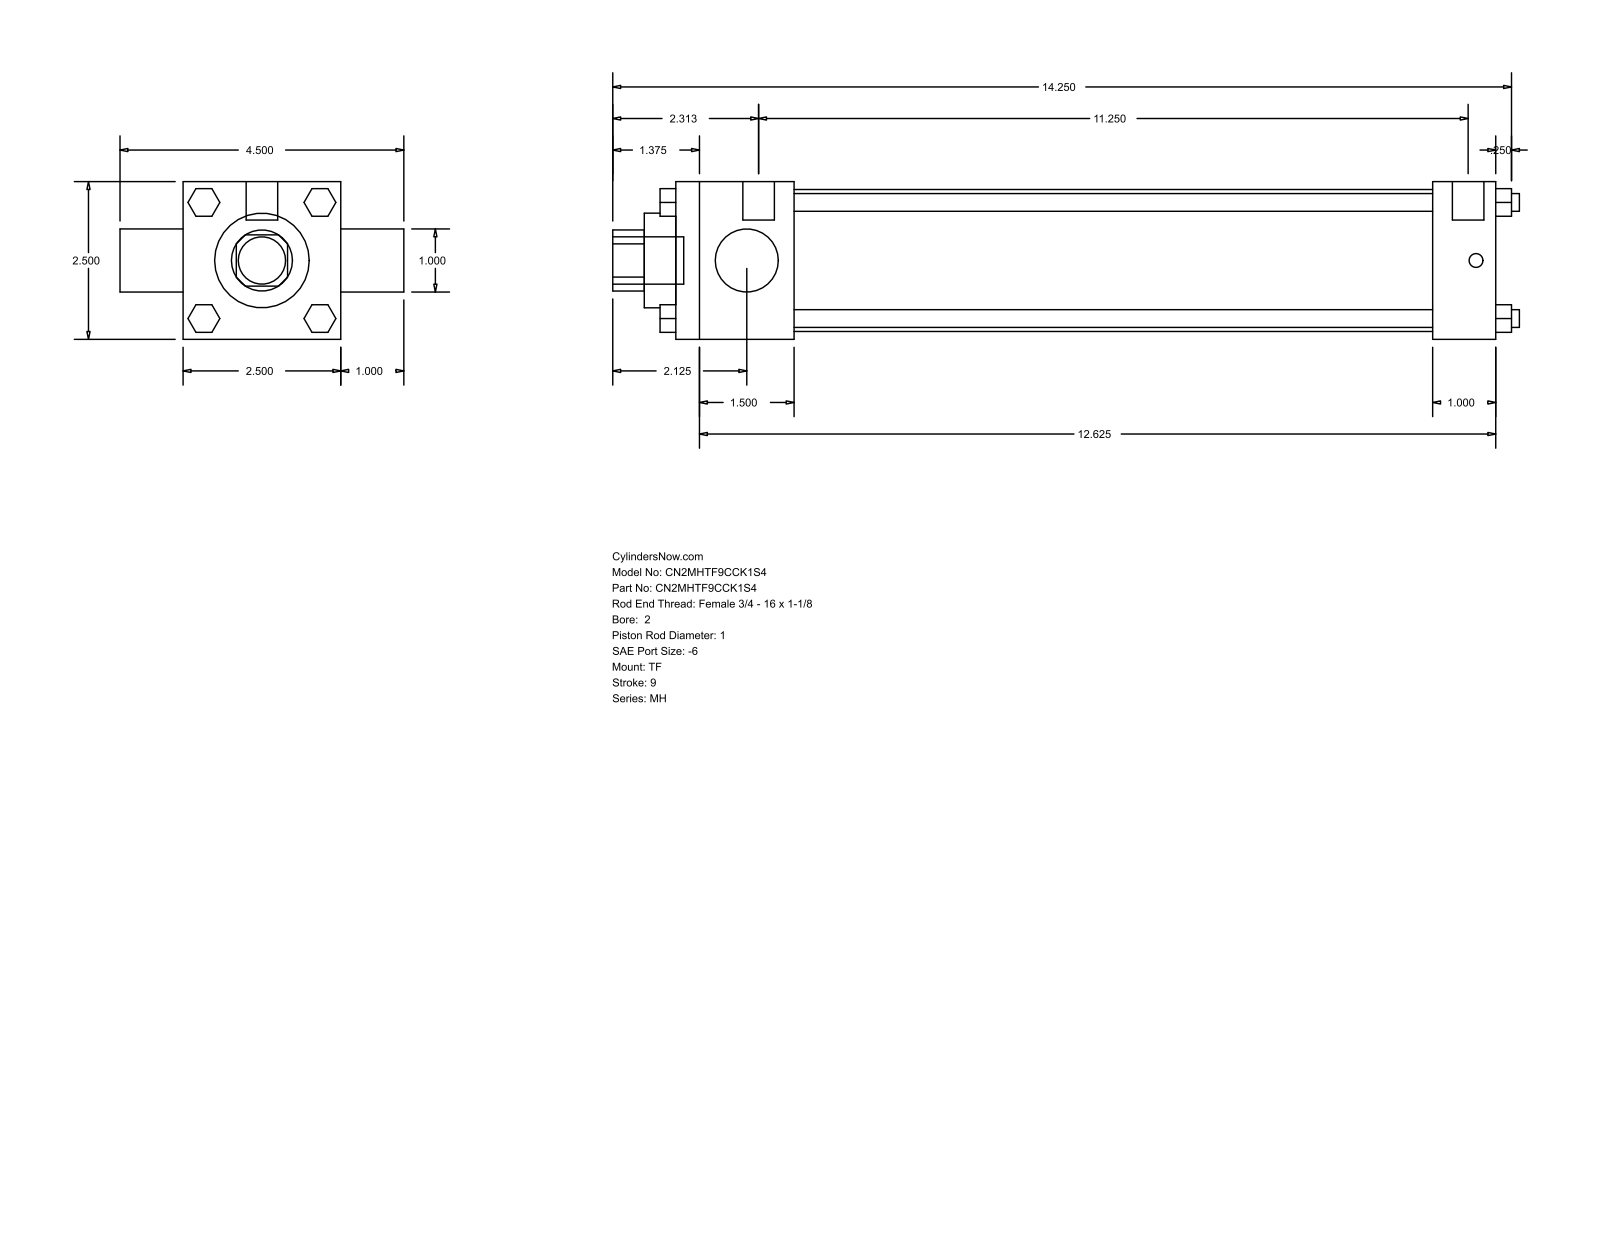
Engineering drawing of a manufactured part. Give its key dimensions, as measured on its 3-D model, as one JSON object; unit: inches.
{"part_name": "MH_TF__0200_1", "step_written_by": "GSSL Pune (CONFIG_CONTROL_DESIGN)", "units": "inches", "bodies": {"solids": 0, "faces": 120, "planar": 92, "cylindrical": 28, "other": 0}, "overall_size": [14.375, 4.5, 2.5], "round_holes": [[1, 2], [1.5, 1], [2.25, 1]], "round_bosses_or_shafts": [[0.281, 4], [0.219, 3], [0.5, 2], [0.75, 1]], "partial_cylinders_radius": [[0.484, 1]], "face_to_face_distances": [2.5, 13, 1, 1.875, 12, 10.125, 11.125, 3.5, 13.5, 0.25]}
